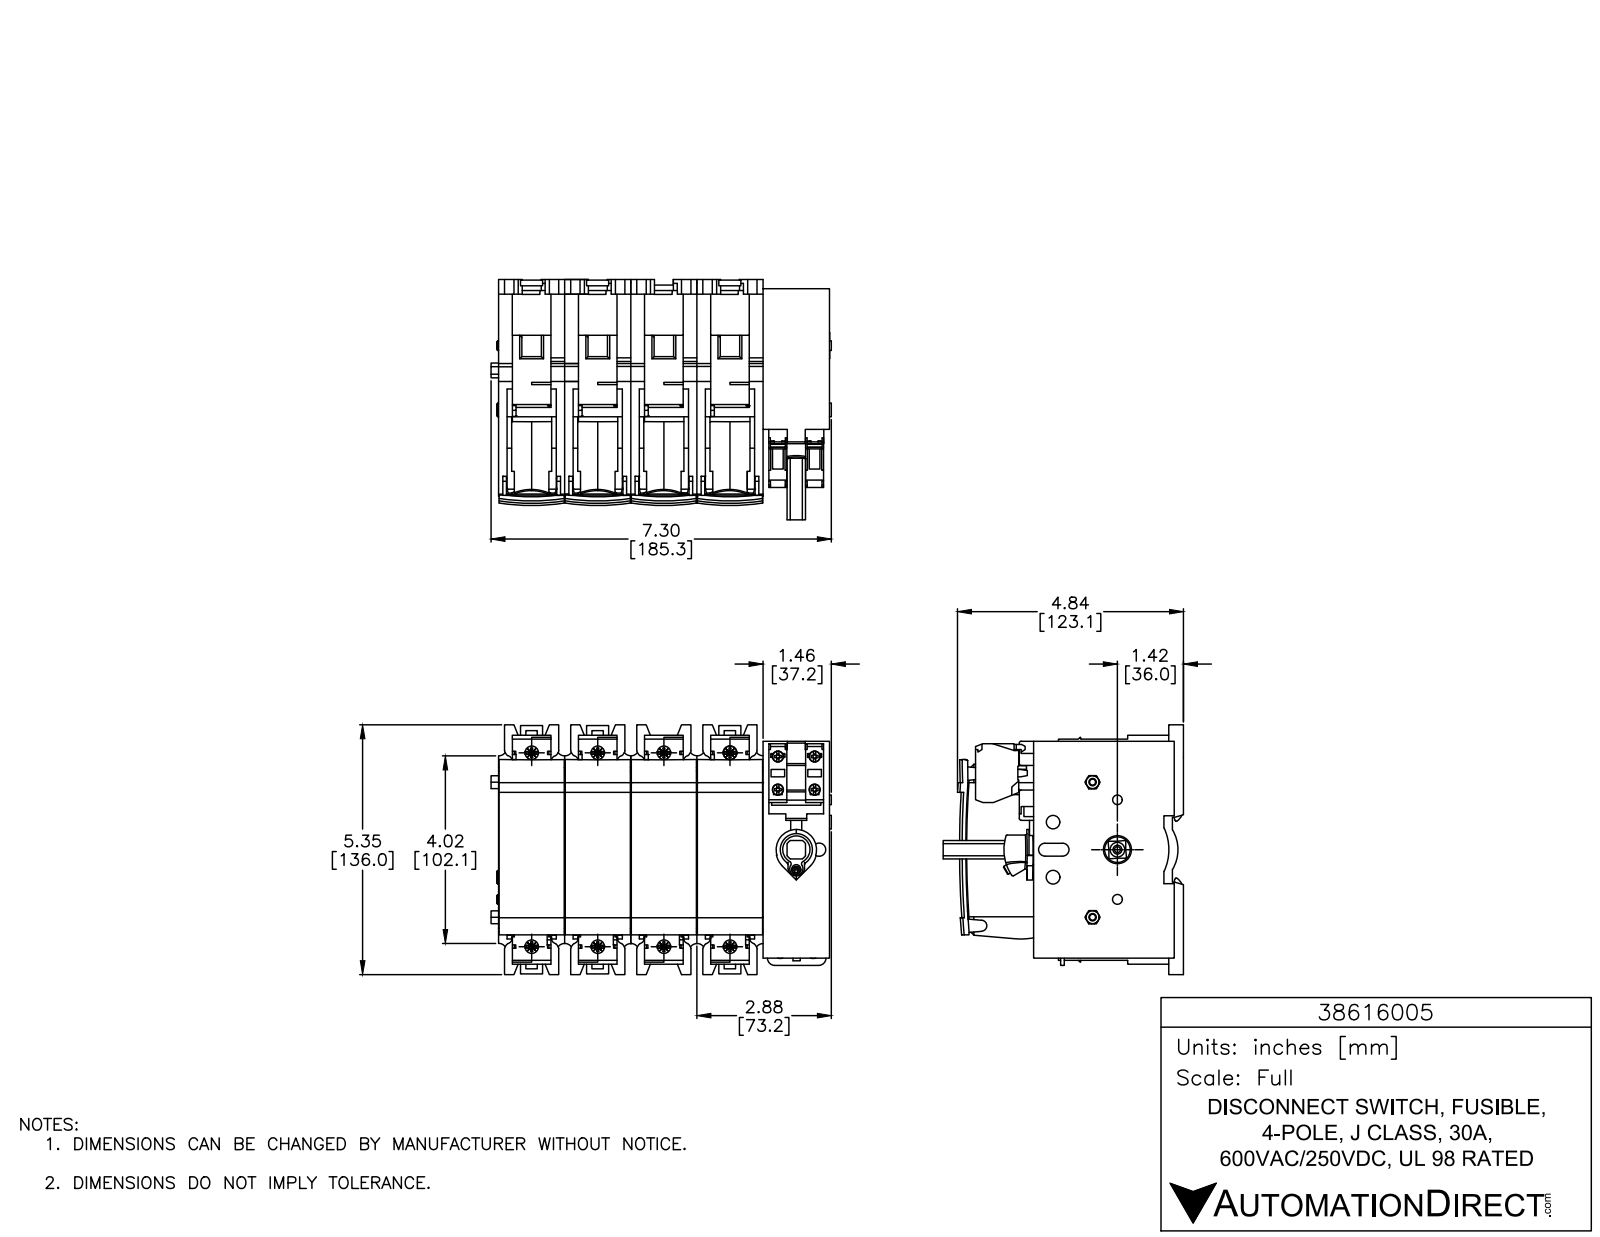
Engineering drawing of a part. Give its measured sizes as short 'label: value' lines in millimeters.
name: 38616005
written by: SolidWorks 2015 (AUTOMOTIVE_DESIGN)
unit: mm
bodies: 15 solids, 2756 faces (1840 planar, 596 cylindrical, 320 other)
size: 182.2 × 136 × 123.1
volume: 1 906 000 mm³; area: 287 600 mm²
holes: 8× ⌀7.4, 2× ⌀2.2, 2× ⌀3.2, 2× ⌀4, 2× ⌀4, 2× ⌀4.3, 2× ⌀5.4, 2× ⌀7.5, 2× ⌀8, 1× ⌀2.5, 1× ⌀3.3, 1× ⌀7.2
bosses: 2× ⌀7.3, 2× ⌀5.2, 1× ⌀16, 1× ⌀8, 1× ⌀5, 1× ⌀3.5
rounds: 84× R0.2, 13× R1, 12× R0.5, 9× R5, 4× R3, 3× R3.5, 2× R1.7, 2× R4
face distances: 36, 72, 108, 7.5, 28.5, 43.5, 64.5, 144, 100.5, 79.5
hole spacings: 36, 111.4, 72, 105.4, 127.7, 16.6, 25.1, 27.1
